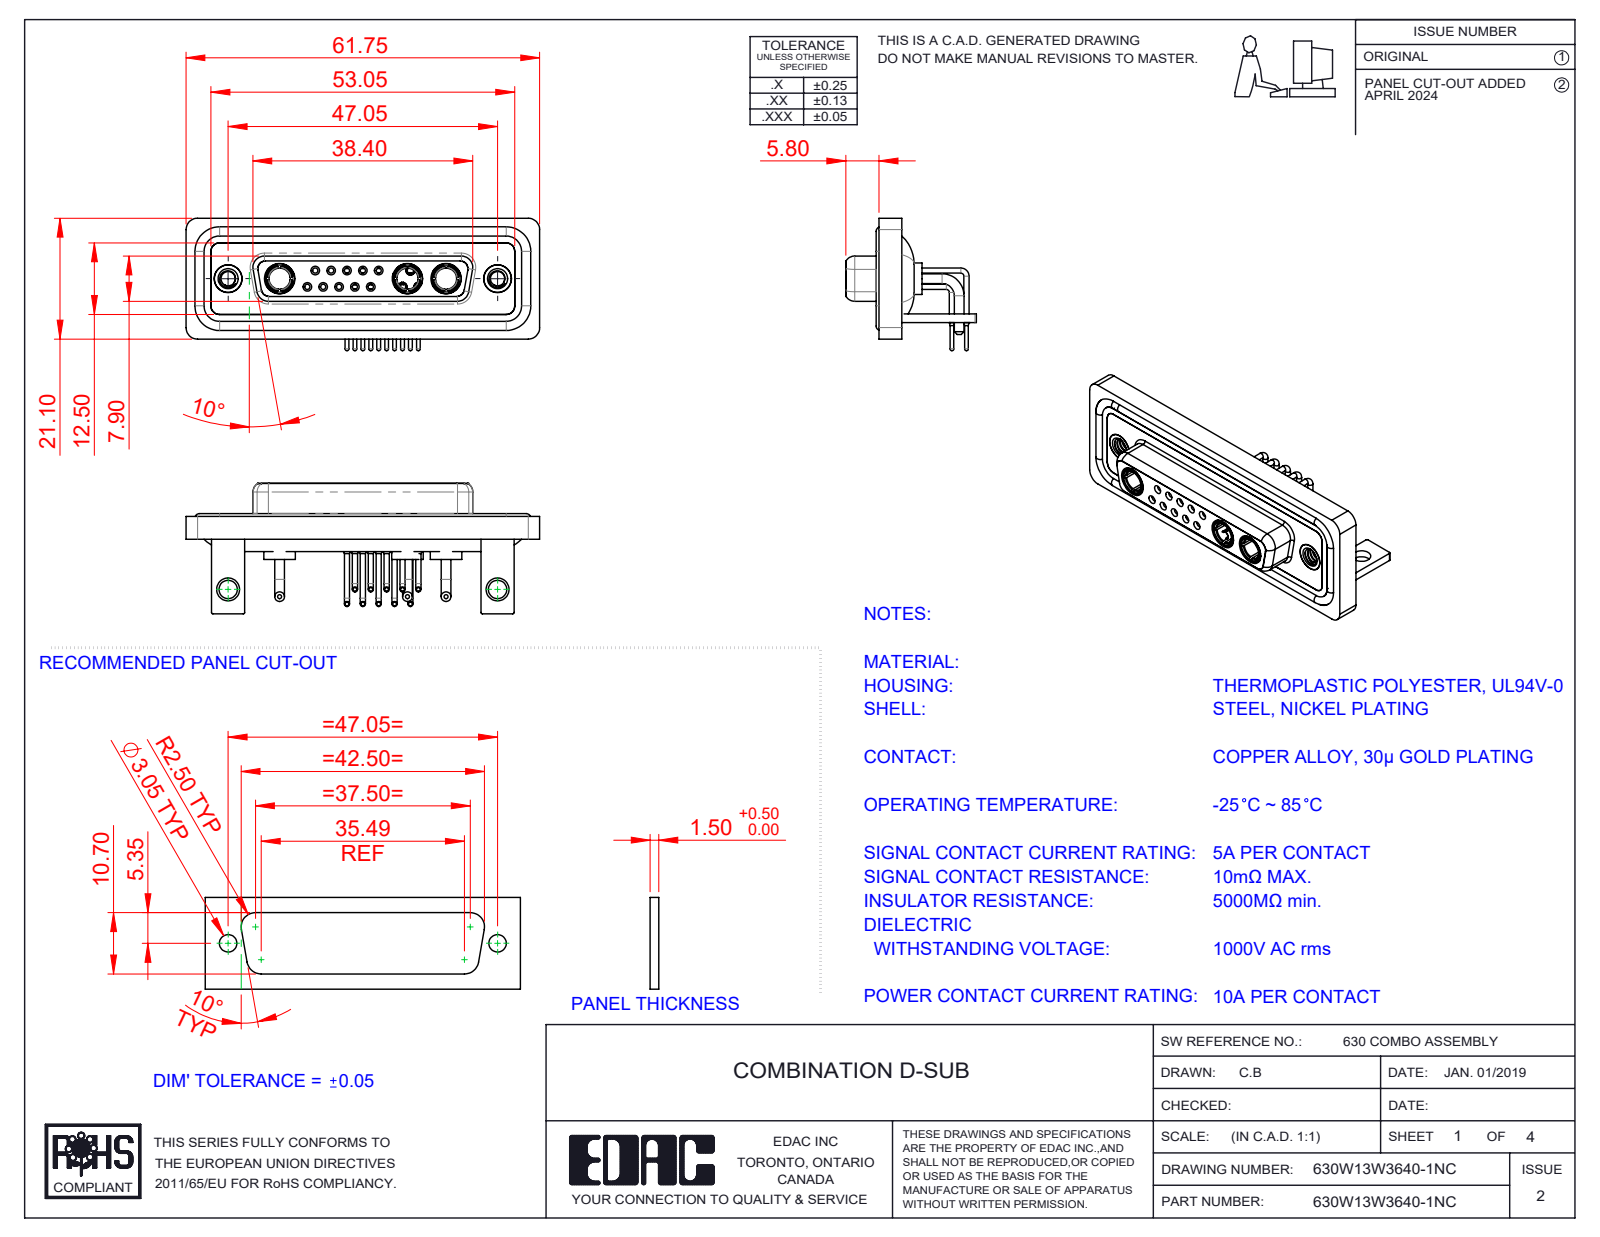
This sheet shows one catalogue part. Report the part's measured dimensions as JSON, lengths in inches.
{"part_name": "630Combo Waterproof Housing_25 Contacts; 630Combo Shell Rear_25 Contacts; 630Combo Contact Row 2_50 Contacts; 630Combo Stabilizer Bracket_50 Contacts (+6 more)", "step_written_by": "SolidWorks 2023 (CONFIG_CONTROL_DESIGN)", "units": "inches", "bodies": {"solids": 25, "faces": 1192, "planar": 362, "cylindrical": 515, "other": 315}, "overall_size": [2.431, 0.91, 0.898], "volume_in3": 0.528, "surface_area_in2": 23.07, "round_holes": [[0.035, 10], [0.043, 10], [0.059, 10], [0.079, 10], [0.063, 5], [0.067, 5], [0.191, 5], [0.146, 3], [0.209, 3], [0.098, 2], [0.126, 2], [0.157, 2]], "round_bosses_or_shafts": [[0.035, 15], [0.063, 12], [0.026, 10], [0.067, 6], [0.079, 5], [0.059, 5], [0.217, 3], [0.205, 3]], "partial_cylinders_radius": [[0.079, 19], [0.059, 18], [0.01, 16], [0.053, 8], [0.063, 8], [0.02, 5], [0.024, 4], [0.026, 4]], "face_to_face_distances": [0.016, 0.071, 0.114, 0.059, 0.146, 0.161, 0.043, 0.055, 0.063, 0.122], "hole_center_spacings": [0.124, 0.109, 0.218, 0.198, 0.327, 0.198, 0.295, 0.436]}
